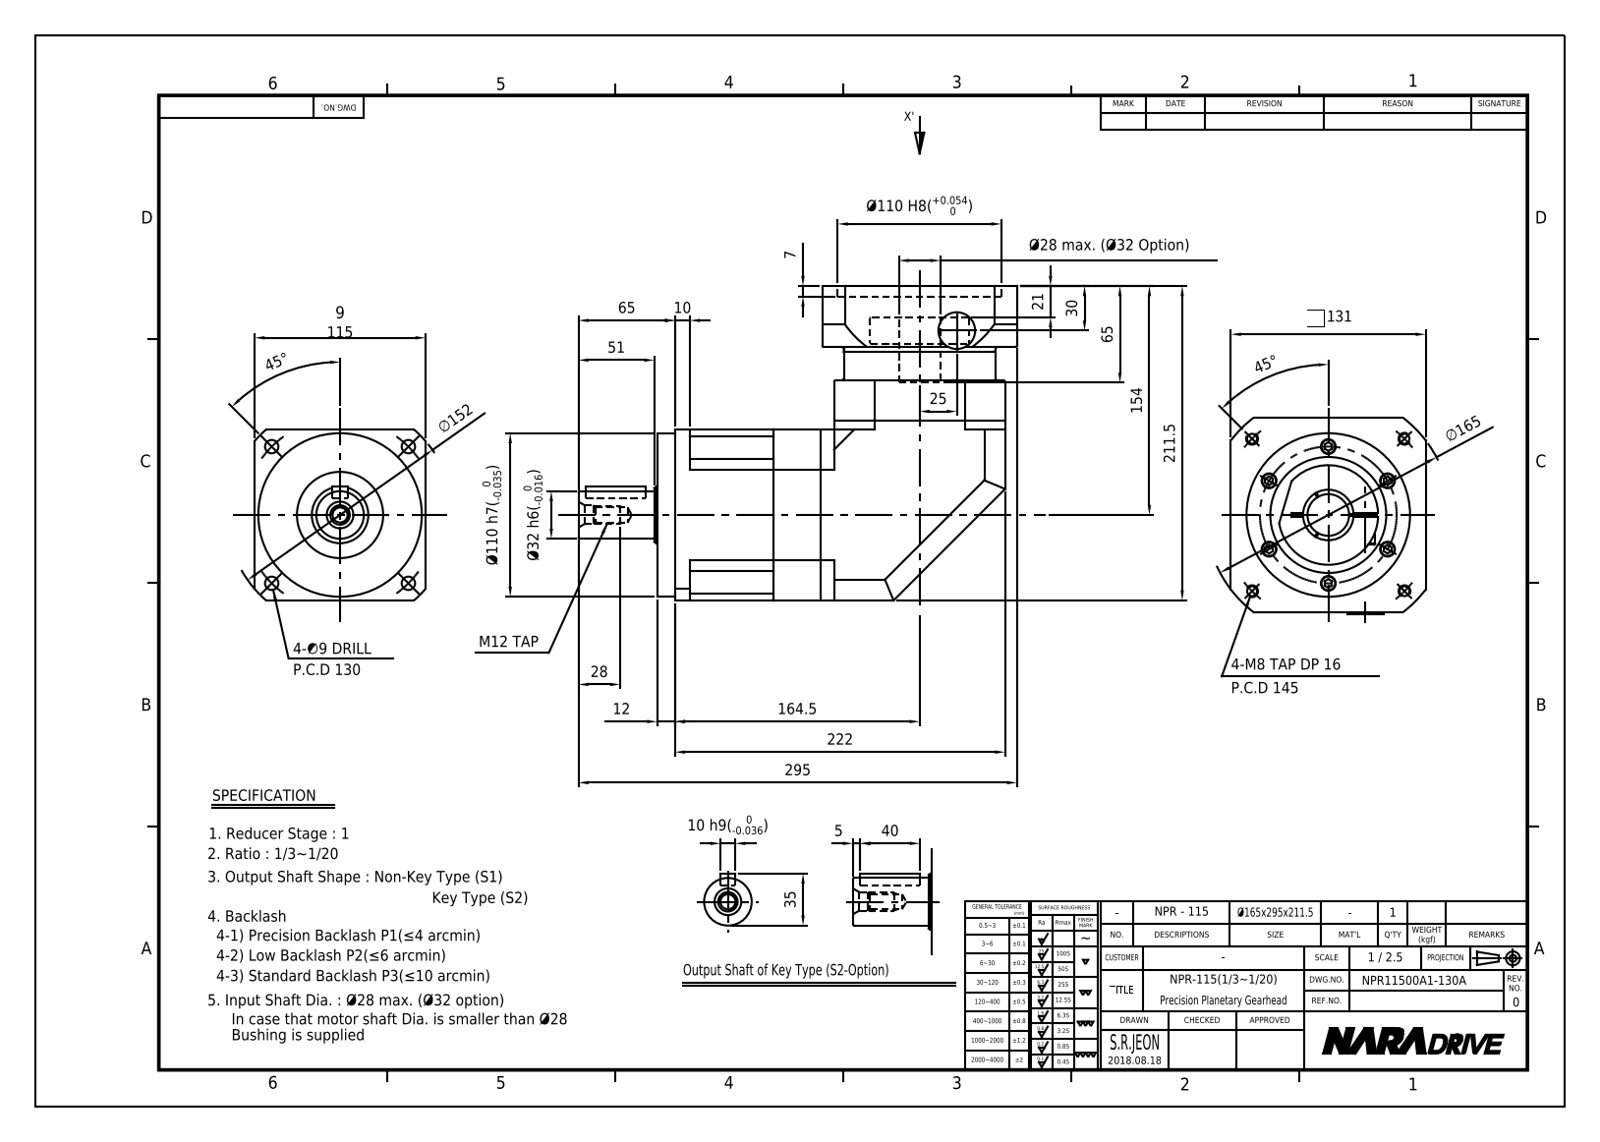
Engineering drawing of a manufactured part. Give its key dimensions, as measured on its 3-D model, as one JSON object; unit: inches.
{"part_name": "NPR11500A1-130A-S1", "step_written_by": "Autodesk Inventor 2015 (AUTOMOTIVE_DESIGN)", "units": "inches", "bodies": {"solids": 2, "faces": 541, "planar": 256, "cylindrical": 161, "other": 124}, "overall_size": [11.614, 8.327, 5.197], "volume_in3": 177.5, "surface_area_in2": 461.5, "round_holes": [[0.194, 10], [0.26, 10], [0.433, 10], [0.163, 8], [0.217, 8], [0.374, 8], [0.262, 5], [0.354, 5], [0.398, 1], [0.404, 1], [0.492, 1], [0.571, 1]], "round_bosses_or_shafts": [[0.394, 10], [0.236, 10], [4.331, 1], [4.016, 1], [2.638, 1], [1.496, 1], [1.26, 1], [0.984, 1]], "partial_cylinders_radius": [[0.039, 8], [0.02, 4], [0.492, 4], [2.559, 2], [0.276, 1], [2.992, 1], [3.248, 1]], "face_to_face_distances": [4.528, 0.315, 4.843, 0.394, 2.677, 5.157, 1.614, 0.079, 2.185, 6.713], "hole_center_spacings": [1.811, 0.684, 2.965, 3.137, 3.656, 3.858, 4.818, 2.3]}
